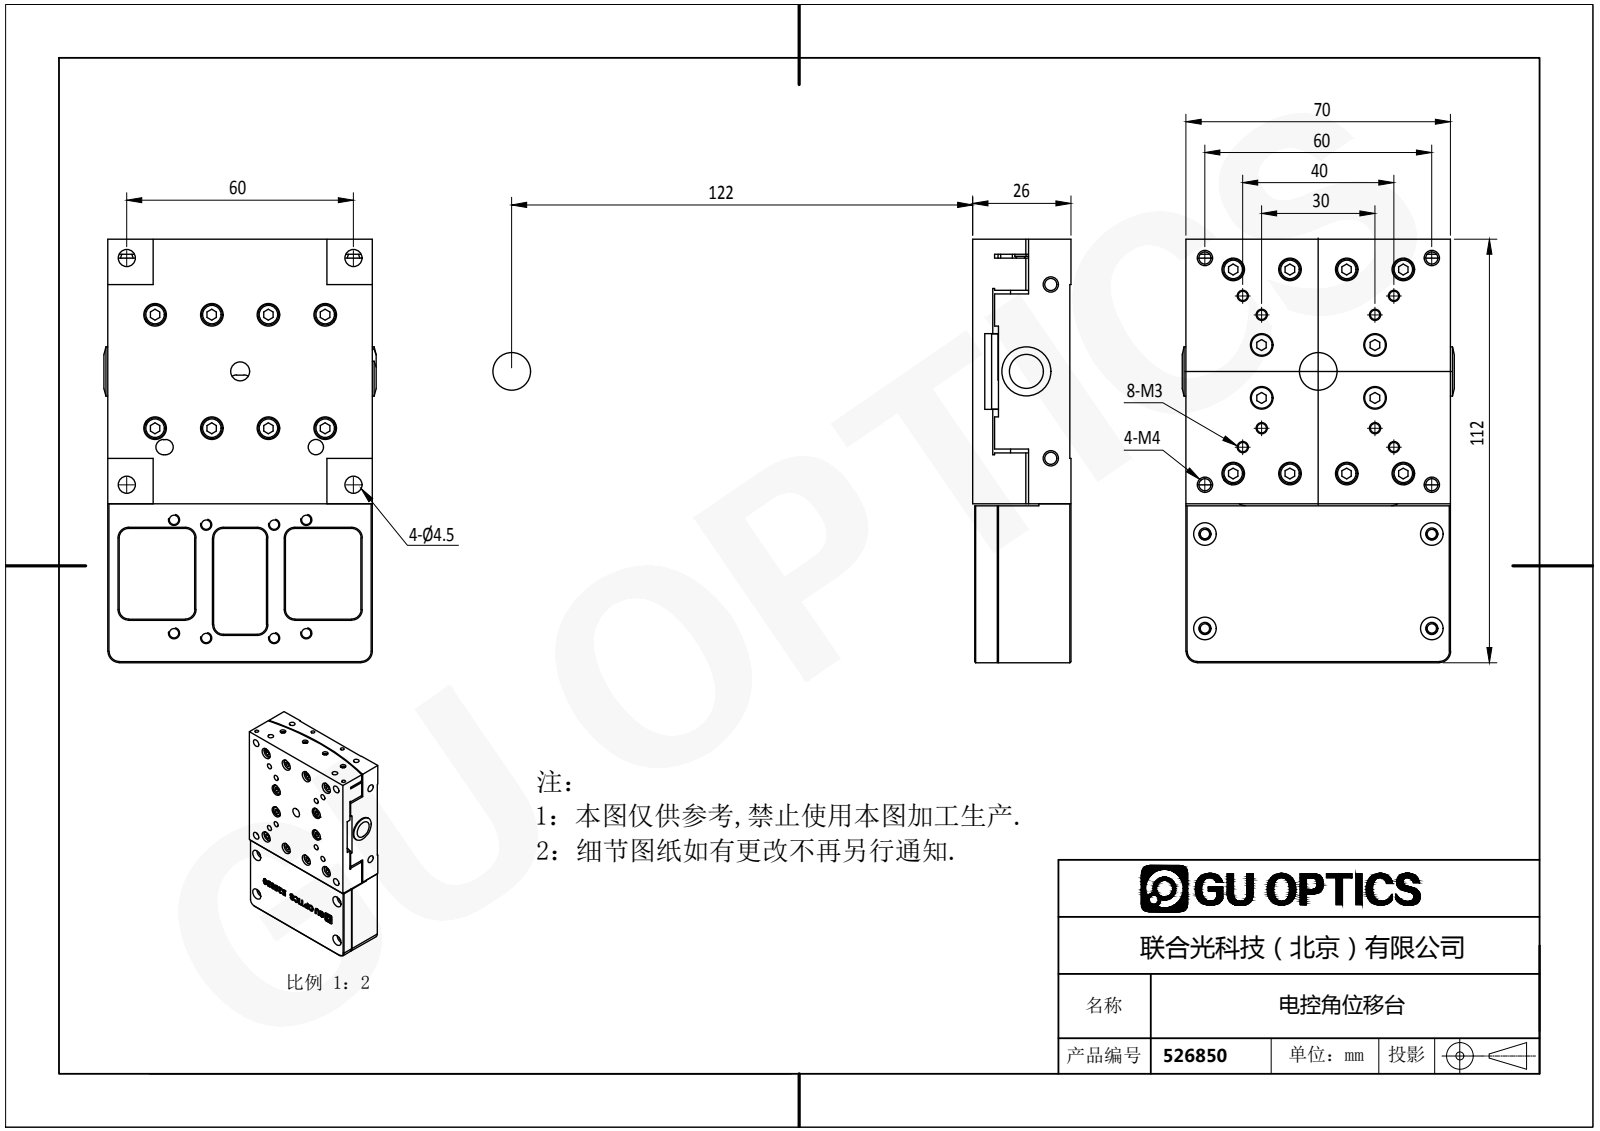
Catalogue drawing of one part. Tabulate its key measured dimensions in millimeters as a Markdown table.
| quantity | value |
| --- | --- |
| STEP written by | SolidWorks 2016 (AUTOMOTIVE_DESIGN) |
| units | millimeters |
| bodies | 0 solids, 1740 faces (639 planar, 598 cylindrical, 503 other) |
| overall size | 153 × 112 × 72 |
| round holes (diameter × count) | 3 × 35, 6 × 26, 3.5 × 20, 2.5 × 17, 2.46 × 12, 4 × 10, 2 × 9, 3.24 × 8, 3.2 × 6, 1.6 × 5, 4.5 × 4, 7.5 × 4 |
| round bosses / shafts (diameter × count) | 5.5 × 20, 3 × 16, 13 × 1 |
| partial cylindrical surfaces (radius × count) | 3 × 13, 2.5 × 12, 2 × 10, 0.79 × 2, 1.23 × 2, 1.5 × 2, 1.62 × 1, 2.25 × 1 |
| main face-to-face distances | 10.5, 1.5, 0.5, 70, 25.7, 4.5, 13.5, 5, 42, 21 |
| hole center spacings | 30, 42.43, 10.97, 16.77, 23.24, 27.04, 27.46, 50.99 |
